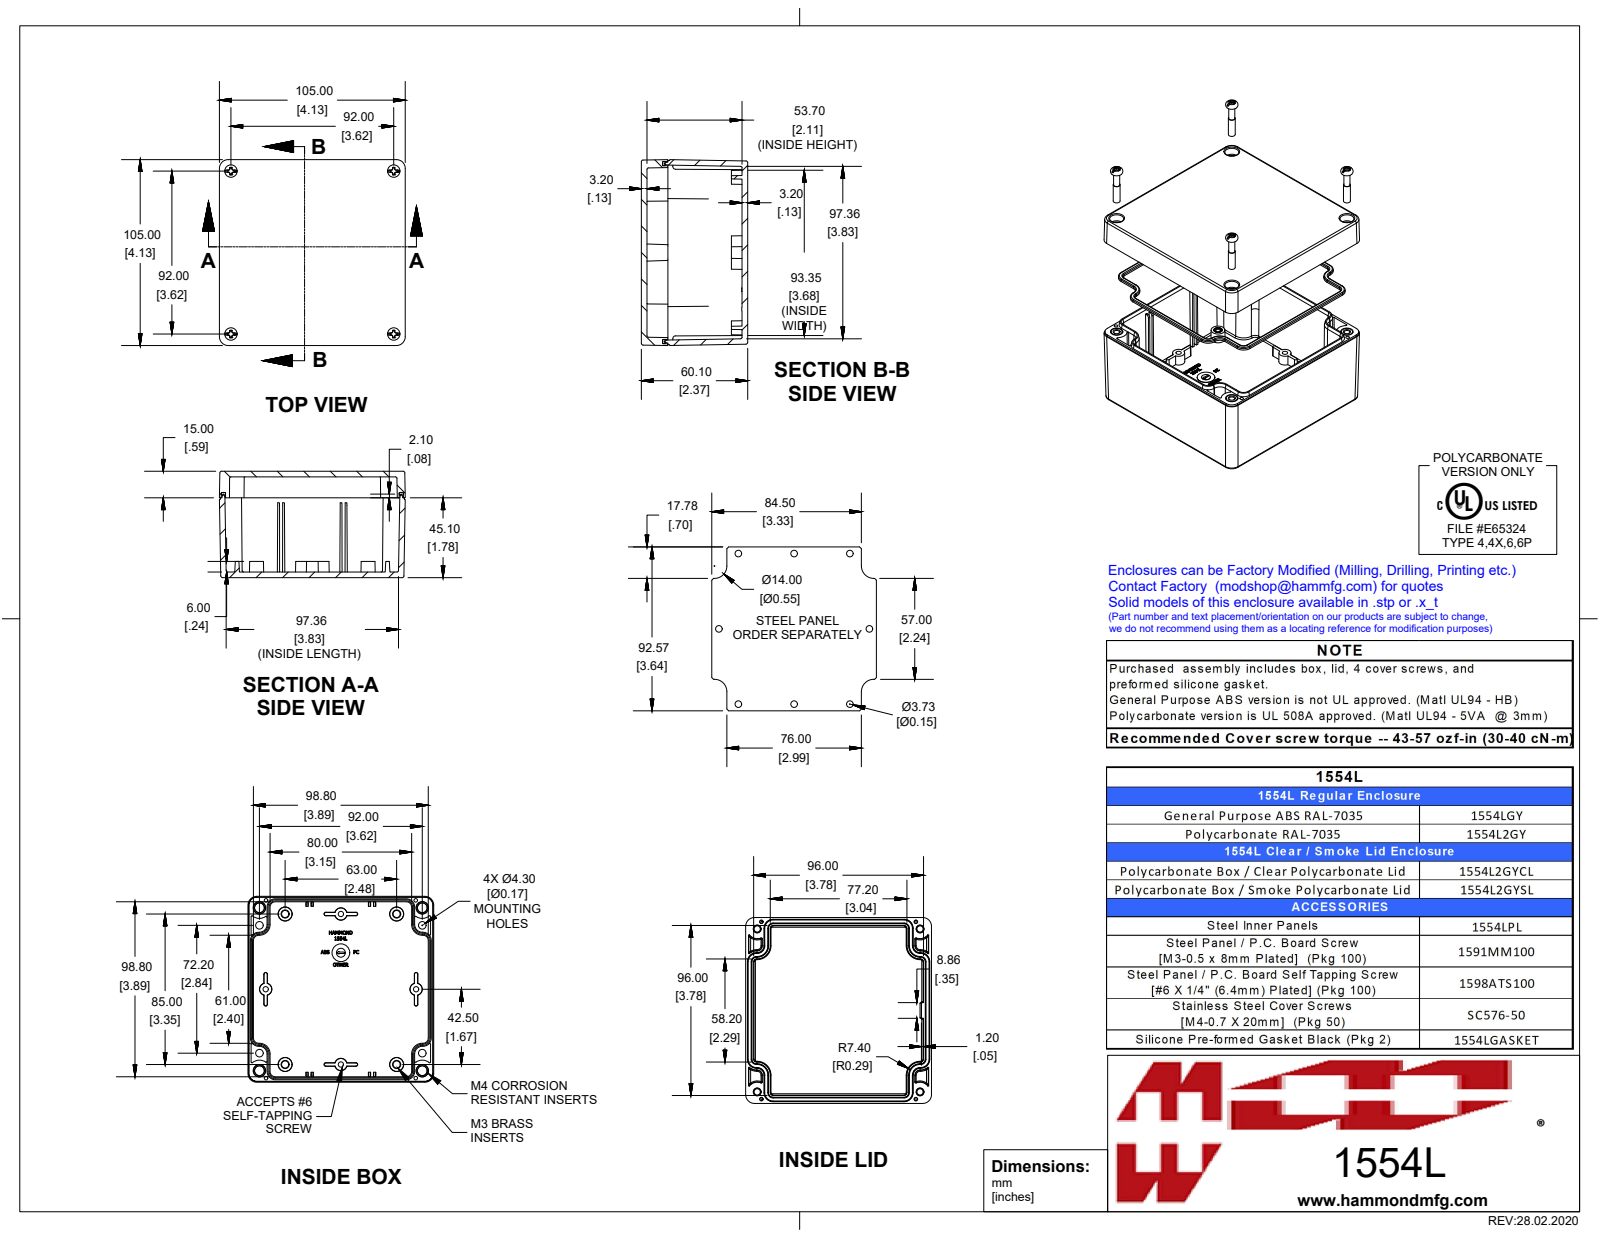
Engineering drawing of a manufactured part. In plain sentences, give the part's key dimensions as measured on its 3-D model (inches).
The part is named "1554LGY". Its 3-D file was written by "SolidWorks 2019 (AUTOMOTIVE_DESIGN)". It is 15 solids with 1851 faces: 612 planar, 374 cylindrical and 865 other. Overall it measures 4.134 by 4.134 by 2.366 inches. Its volume is 9.697 cubic inches and its surface area 173.6 square inches. Round holes: 4 of diameter 0.097, 4 of diameter 0.128, 4 of diameter 0.181. Round bosses or shafts: 4 of diameter 0.25, 4 of diameter 0.218, 4 of diameter 0.21, 4 of diameter 0.19, 4 of diameter 0.154, 4 of diameter 0.153, 4 of diameter 0.15, 4 of diameter 0.135. Partial cylindrical surfaces (rounded edges, fillets, slot ends): 26 of radius 0.02, 20 of radius 0.012, 12 of radius 0.039, 10 of radius 0.031, 8 of radius 0.104, 8 of radius 0.197, 8 of radius 0.199, 4 of radius 0.118. The main face-to-face distances are 0.126, 2.24, 0.122, 2.366, 2.114, 4.012, 4.134, 3.957, 0.177, 3.835. The hole center spacings are 0.587, 3.054, 3.531, 3.622, 4.631, 2.48, 3.346, 4.165.
